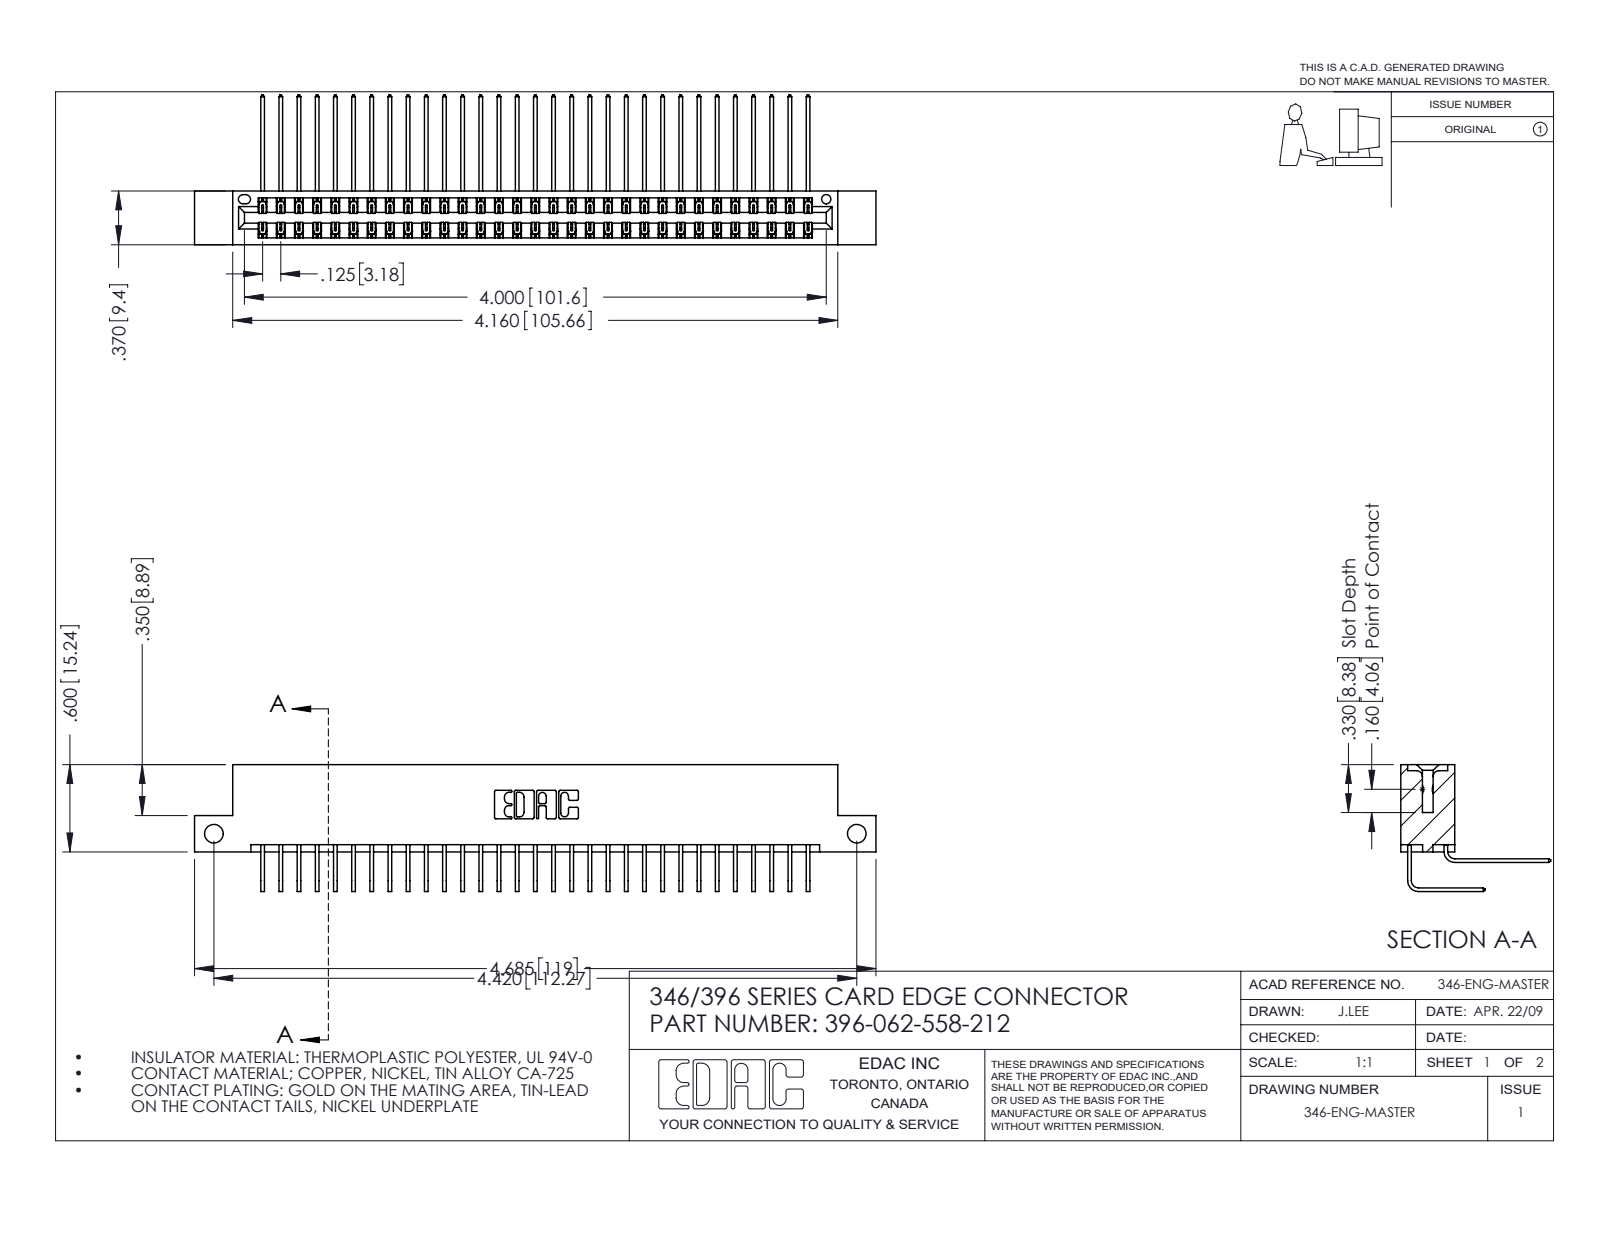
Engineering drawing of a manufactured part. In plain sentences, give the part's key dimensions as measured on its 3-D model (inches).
The part is named "346 Part_Flush Mounting Lugs - Side Mount; 396-062-558-212; 345-292-001_558 Tail - 2; 345-292-001_558 559 Tail - 1". Its 3-D file was written by "SolidWorks 2016 (CONFIG_CONTROL_DESIGN)". It is 63 solids with 3470 faces: 2370 planar, 1100 cylindrical and 0 other. Overall it measures 4.685 by 1.03 by 0.873 inches. Its volume is 0.719 cubic inches and its surface area 27.3 square inches. Round holes: 2 of diameter 0.128, 1 of diameter 0.064. Partial cylindrical surfaces (rounded edges, fillets, slot ends): 93 of radius 0.006, 22 of radius 0.01, 6 of radius 0.007, 6 of radius 0.031, 3 of radius 0.026, 2 of radius 0.014, 2 of radius 0.022, 2 of radius 0.024. The main face-to-face distances are 0.322, 0.048, 0.025, 0.25, 0.37, 0.298, 0.072, 0.275, 0.148, 0.222. The hole center spacings are 4.42.
